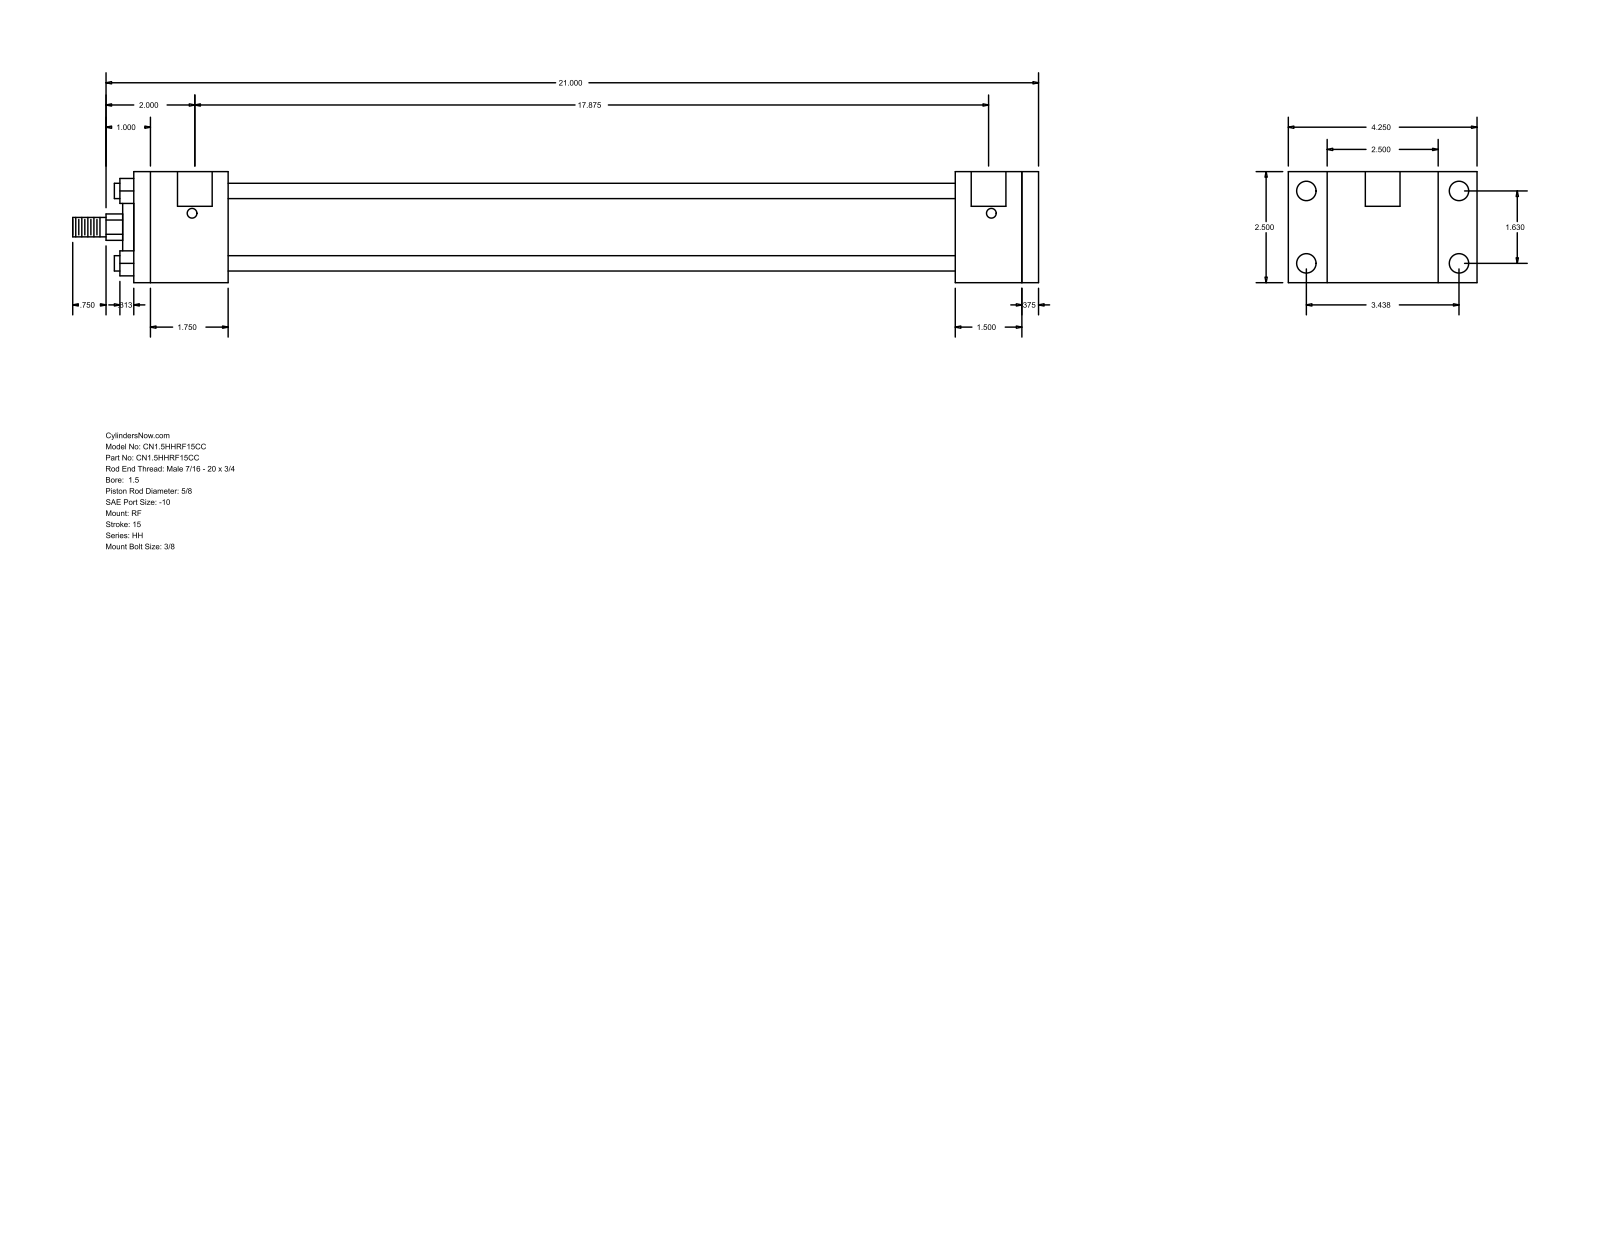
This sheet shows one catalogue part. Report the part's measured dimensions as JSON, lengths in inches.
{"part_name": "HH_RF__0150_0.625", "step_written_by": "GSSL Pune (CONFIG_CONTROL_DESIGN)", "units": "inches", "bodies": {"solids": 0, "faces": 92, "planar": 64, "cylindrical": 28, "other": 0}, "overall_size": [21.75, 4.25, 2.5], "round_holes": [[0.219, 4], [0.438, 4], [0.781, 2]], "round_bosses_or_shafts": [[0.345, 4], [1.75, 1], [1.125, 1], [0.625, 1], [0.437, 1]], "partial_cylinders_radius": [[0.297, 1]], "face_to_face_distances": [2.5, 20.375, 20, 0.375, 1.875, 2.125, 18.5, 16.375, 17.875, 18.25], "hole_center_spacings": [0.063, 1.63, 3.438, 3.805, 17.937, 18, 17.875]}
